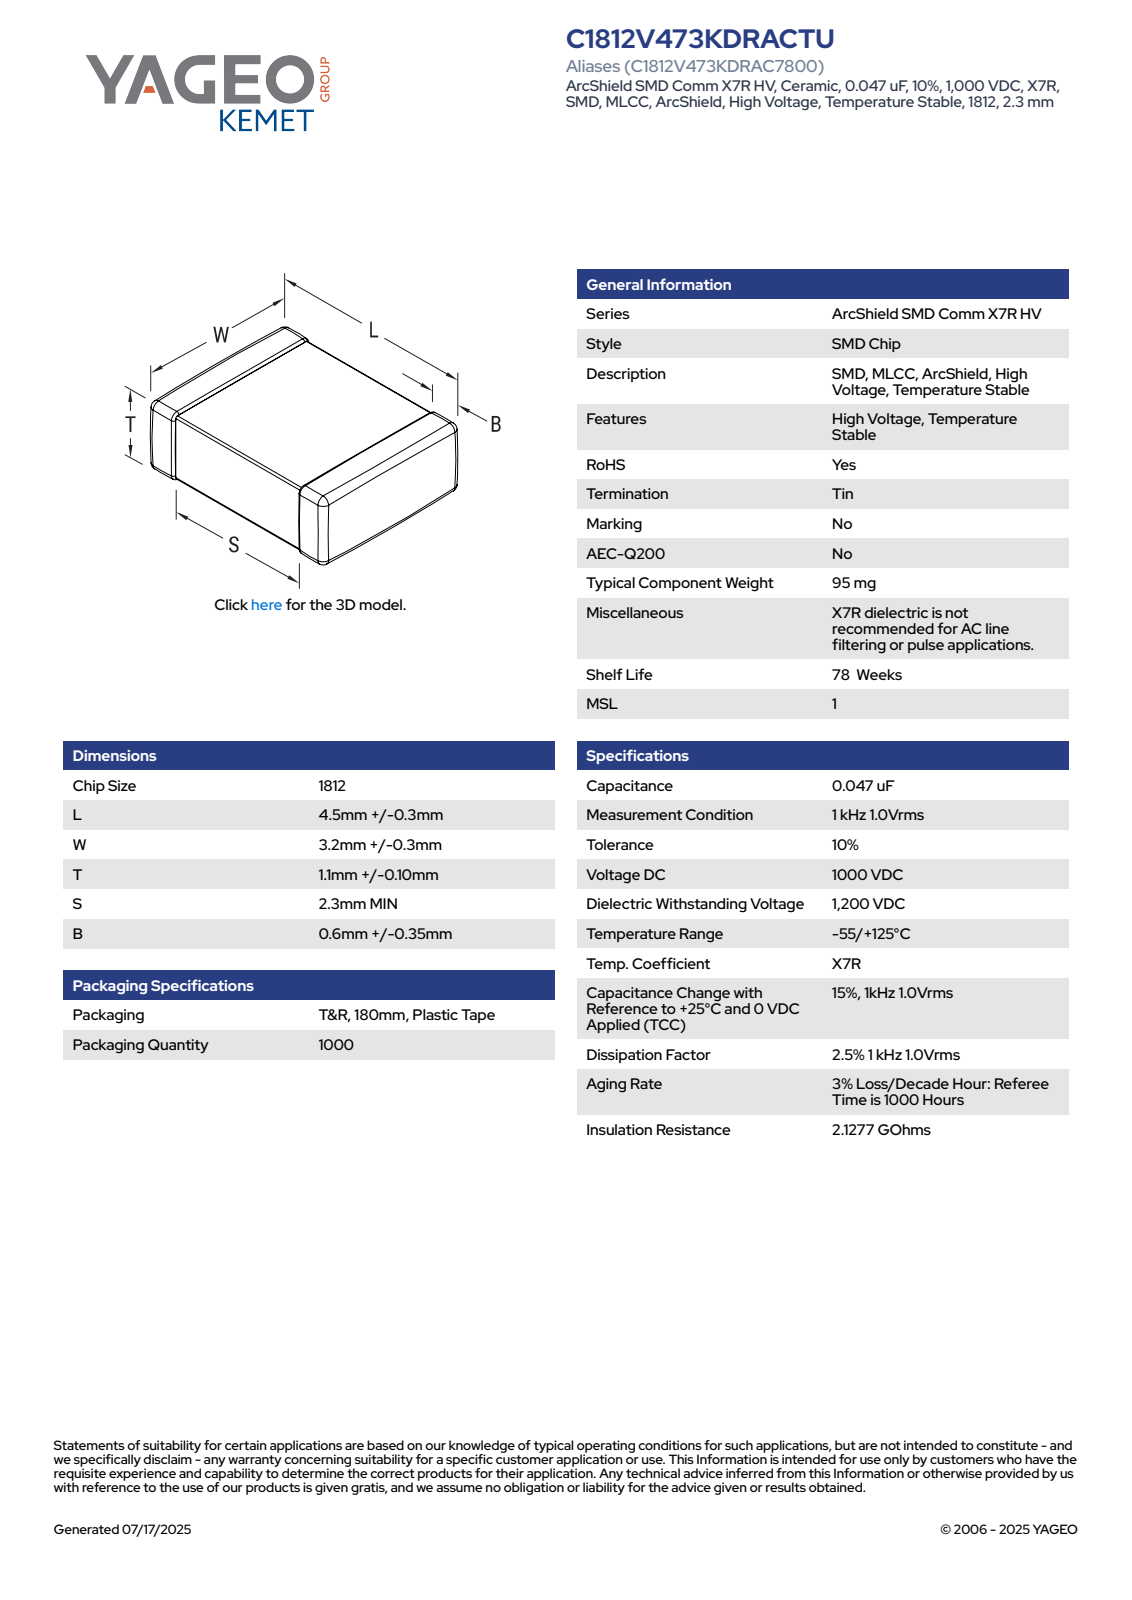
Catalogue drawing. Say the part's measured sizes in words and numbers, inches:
The part is named "CCS_CCSTDNOS_1812_L4.8W3.5T1.2B0.95". Its 3-D file was written by "SolidWorks 2014 (AUTOMOTIVE_DESIGN)". It is 4 solids with 121 faces: 71 planar, 34 cylindrical and 16 other. Overall it measures 0.189 by 0.138 by 0.047 inches. Its volume is 0.001 cubic inches and its surface area 0.081 square inches. The main face-to-face distances are 0.044, 0.042, 0.047, 0.189, 0.135, 0.132, 0.138, 0.059, 0.013, 0.076.
